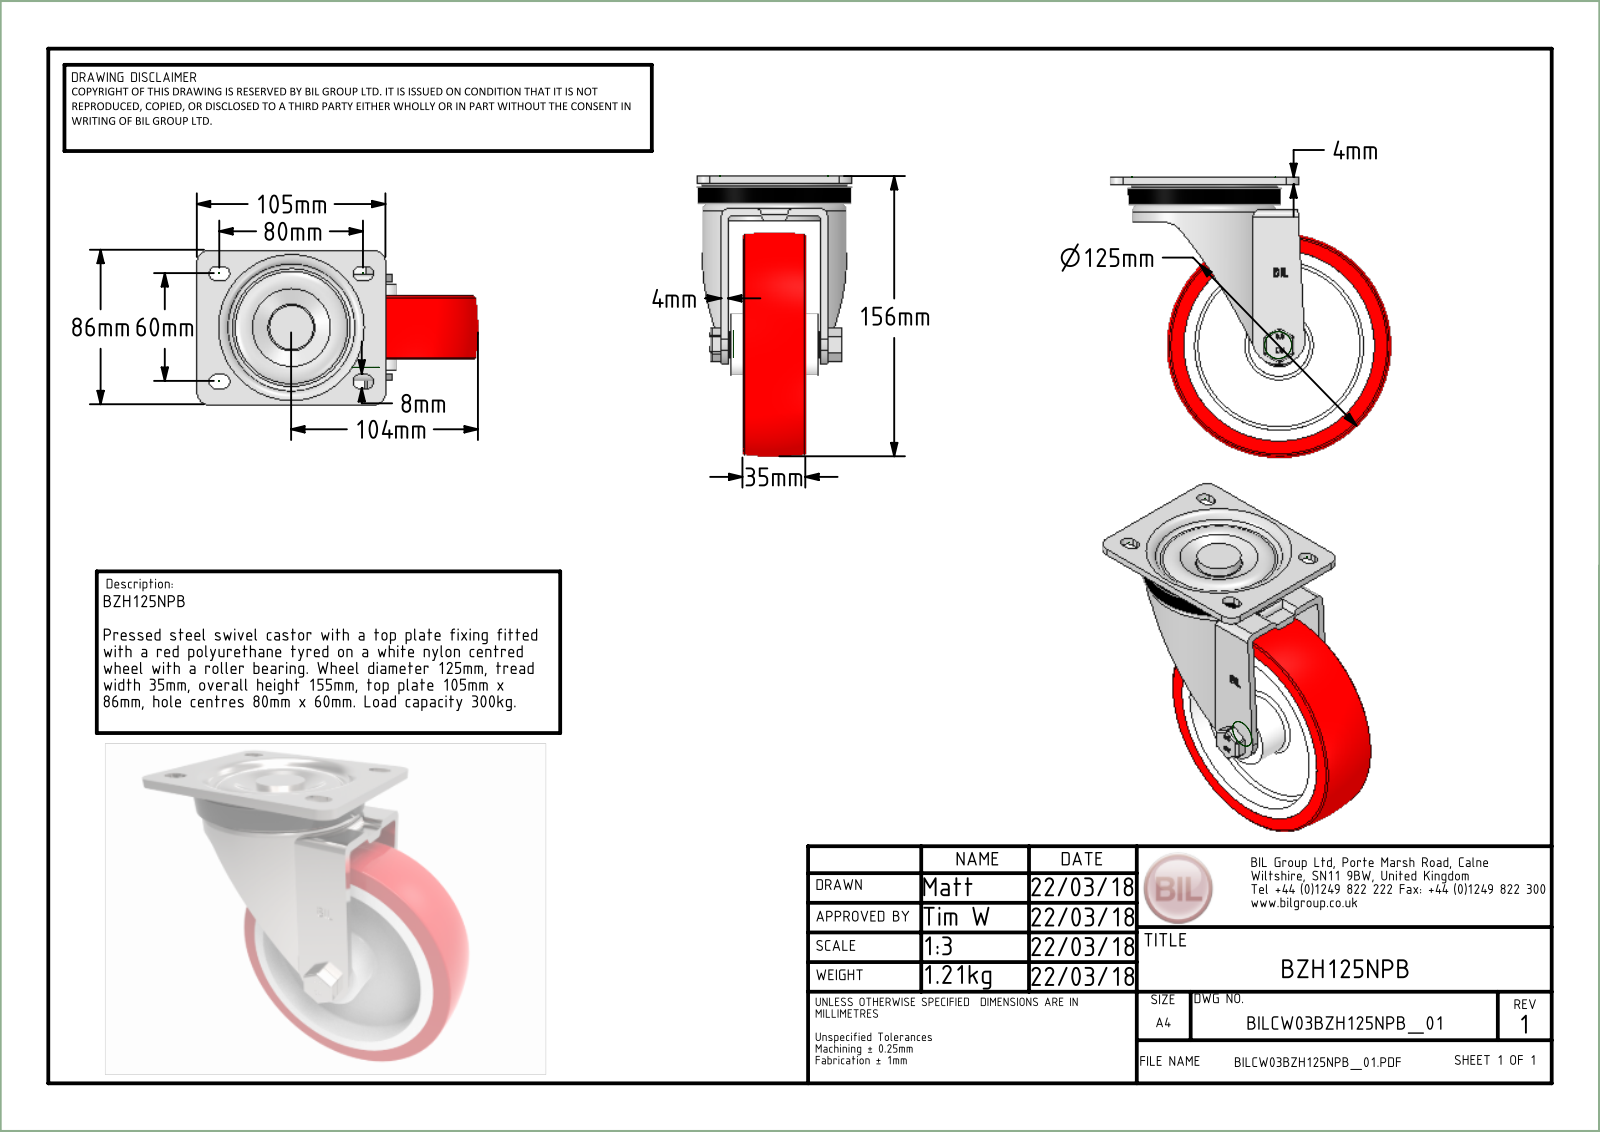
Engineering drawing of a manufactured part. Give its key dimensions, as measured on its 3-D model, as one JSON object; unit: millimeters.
{"part_name": "BZH125NPB v4; BZH125AS - 2 v2; ZINC PLATED, PRESSED STEEL TOP PLATE; ZINC PLATED, PRESSED STEEL FORKS (+8 more)", "step_written_by": "Autodesk Translation Framework v13.20.0.188 (AP242_MANAGED_MODEL_BASED_3D_ENGINEERING_MIM_LF)", "units": "millimeters", "bodies": {"solids": 20, "faces": 489, "planar": 250, "cylindrical": 150, "other": 89}, "overall_size": [156.5, 155, 86], "volume_mm3": 385482, "surface_area_mm2": 161808, "round_holes": [[10, 1], [10.2, 1], [10.5, 1], [12, 1], [15.2, 1], [15.5, 1], [23.5, 1], [25, 1], [27.2, 1], [32, 1], [72, 1], [97, 1]], "round_bosses_or_shafts": [[4, 9], [80, 1], [62, 1], [50.5, 1], [34, 1], [31, 1], [27, 1], [22, 1]], "partial_cylinders_radius": [[0.5, 18], [4.5, 8], [0.75, 6], [2, 4], [8, 4], [4, 2], [21.52, 2], [9.5, 1]], "face_to_face_distances": [4, 15, 7.5, 21, 11.5, 6, 22.5, 26.5, 47.5, 32.5]}
